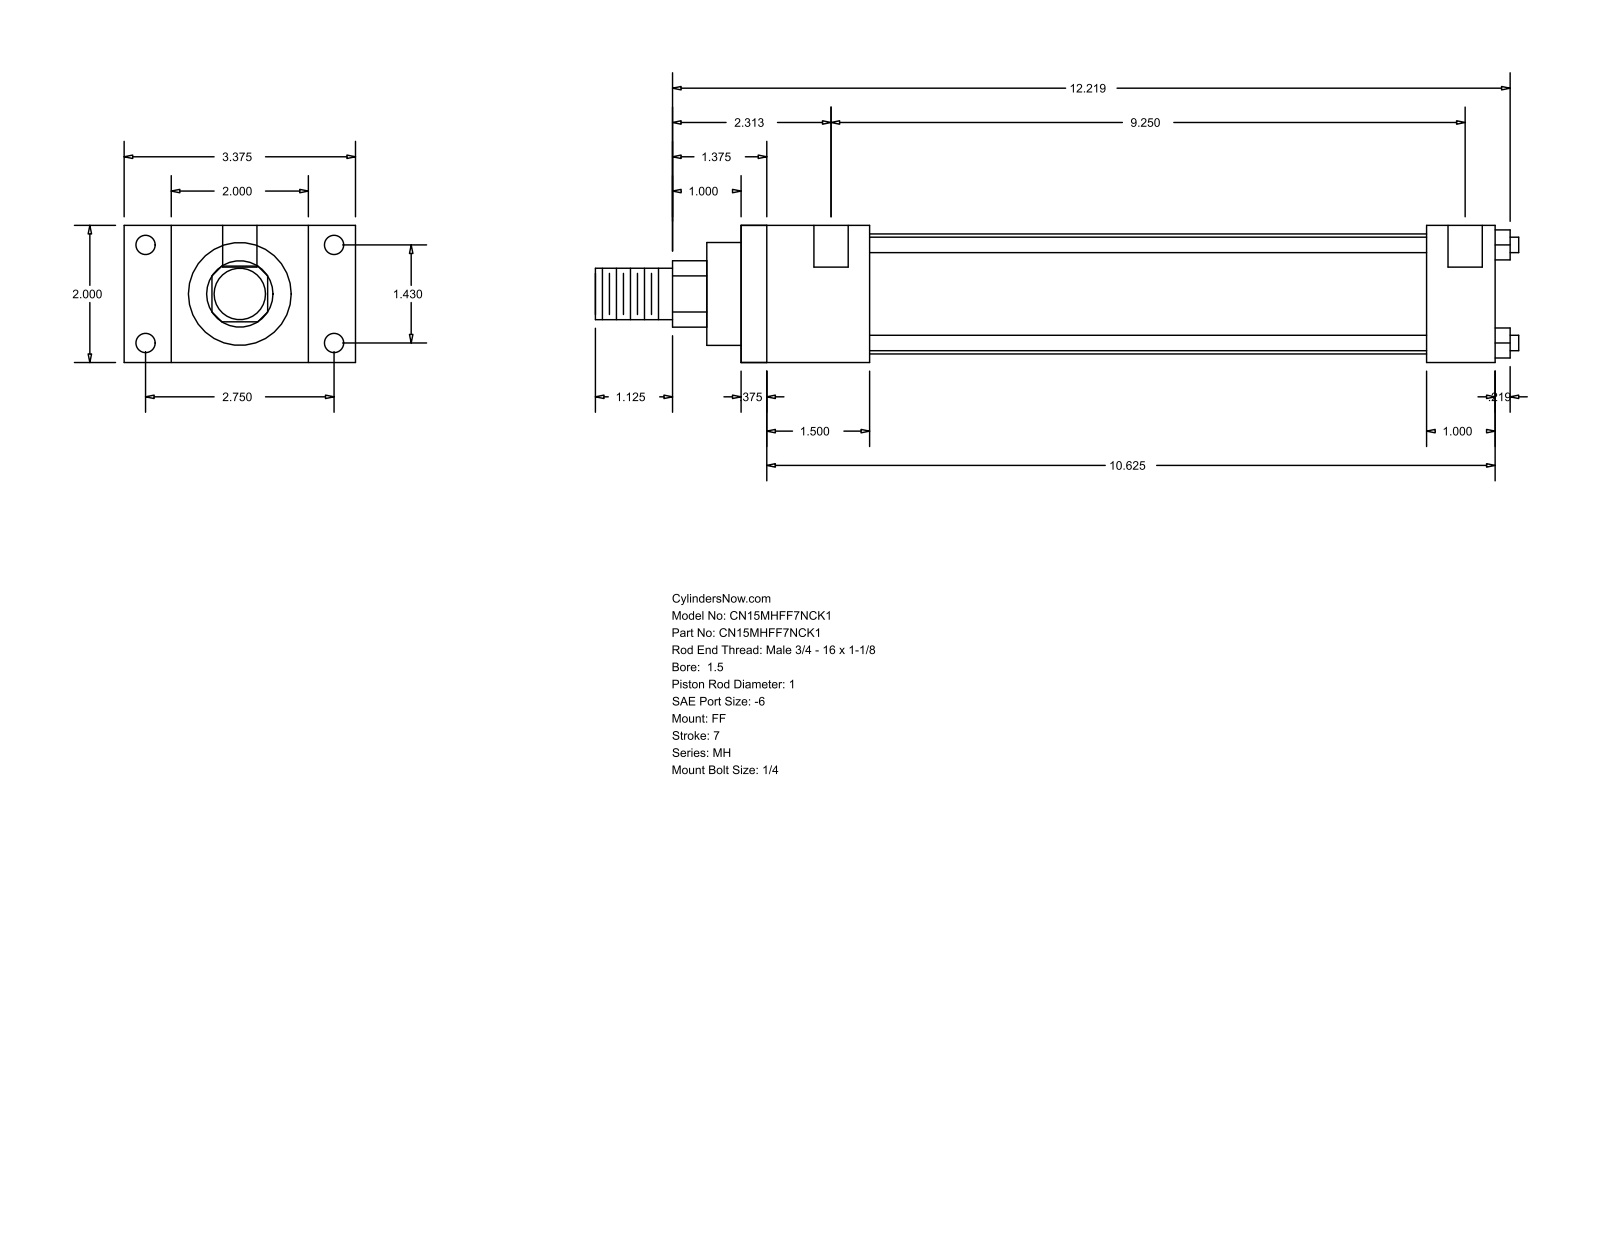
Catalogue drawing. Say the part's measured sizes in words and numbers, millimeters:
The part is named "MH_FF__0150_1". Its 3-D file was written by "GSSL Pune (CONFIG_CONTROL_DESIGN)". It is 0 solids with 92 faces: 64 planar, 28 cylindrical and 0 other. Overall it measures 342.11 by 85.72 by 50.8 millimeters. Round holes: 4 of diameter 5.56, 4 of diameter 7.14, 2 of diameter 12.7. Round bosses or shafts: 4 of diameter 5.71, 1 of diameter 44.45, 1 of diameter 38.1, 1 of diameter 25.4, 1 of diameter 19.05. Partial cylindrical surfaces (rounded edges, fillets, slot ends): 1 of radius 12.29. The main face-to-face distances are 50.8, 279.4, 9.52, 269.88, 25.4, 17.46, 68.26, 47.63, 38.11, 231.77. The hole center spacings are 36.32, 69.84, 78.72, 238.13, 3.18, 234.95.
